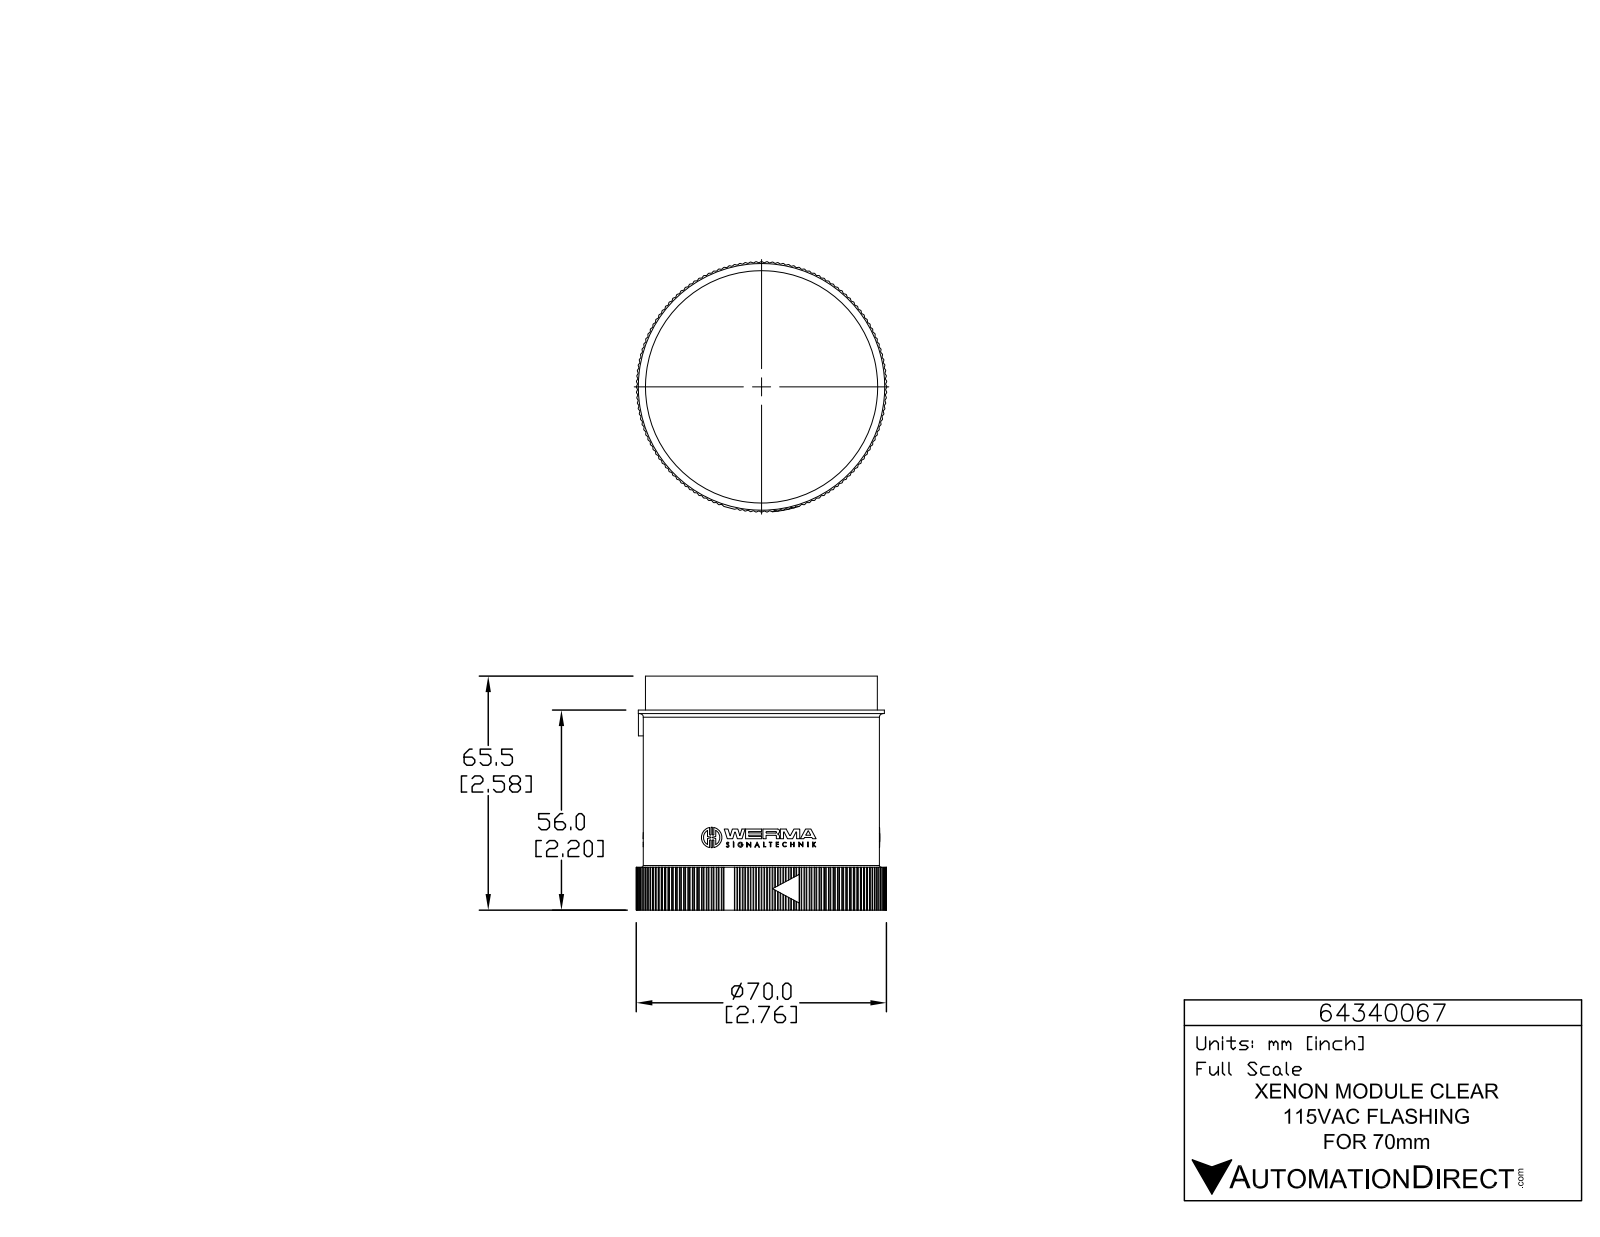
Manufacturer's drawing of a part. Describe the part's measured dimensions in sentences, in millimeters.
The part is named "64350067". Its 3-D file was written by "SolidWorks 2015 (AUTOMOTIVE_DESIGN)". It is 1 solid with 1400 faces: 832 planar, 563 cylindrical and 5 other. Overall it measures 70.2 by 70.2 by 65.5 millimeters. Its volume is 197 000 cubic millimeters and its surface area 24 180 square millimeters. Round holes: 3 of diameter 1, 1 of diameter 65.4. Round bosses or shafts: 3 of diameter 5.7, 3 of diameter 1.4, 1 of diameter 69, 1 of diameter 66.2, 1 of diameter 65. Partial cylindrical surfaces (rounded edges, fillets, slot ends): 285 of radius 0.2, 6 of radius 0.2, 6 of radius 0.2, 6 of radius 0.2, 6 of radius 3.3, 3 of radius 0.1, 3 of radius 0.1, 3 of radius 0.2. The main face-to-face distances are 55.9, 62.3, 9.6, 65.5, 56, 46.4, 9.5, 62.3, 12, 2.4.
